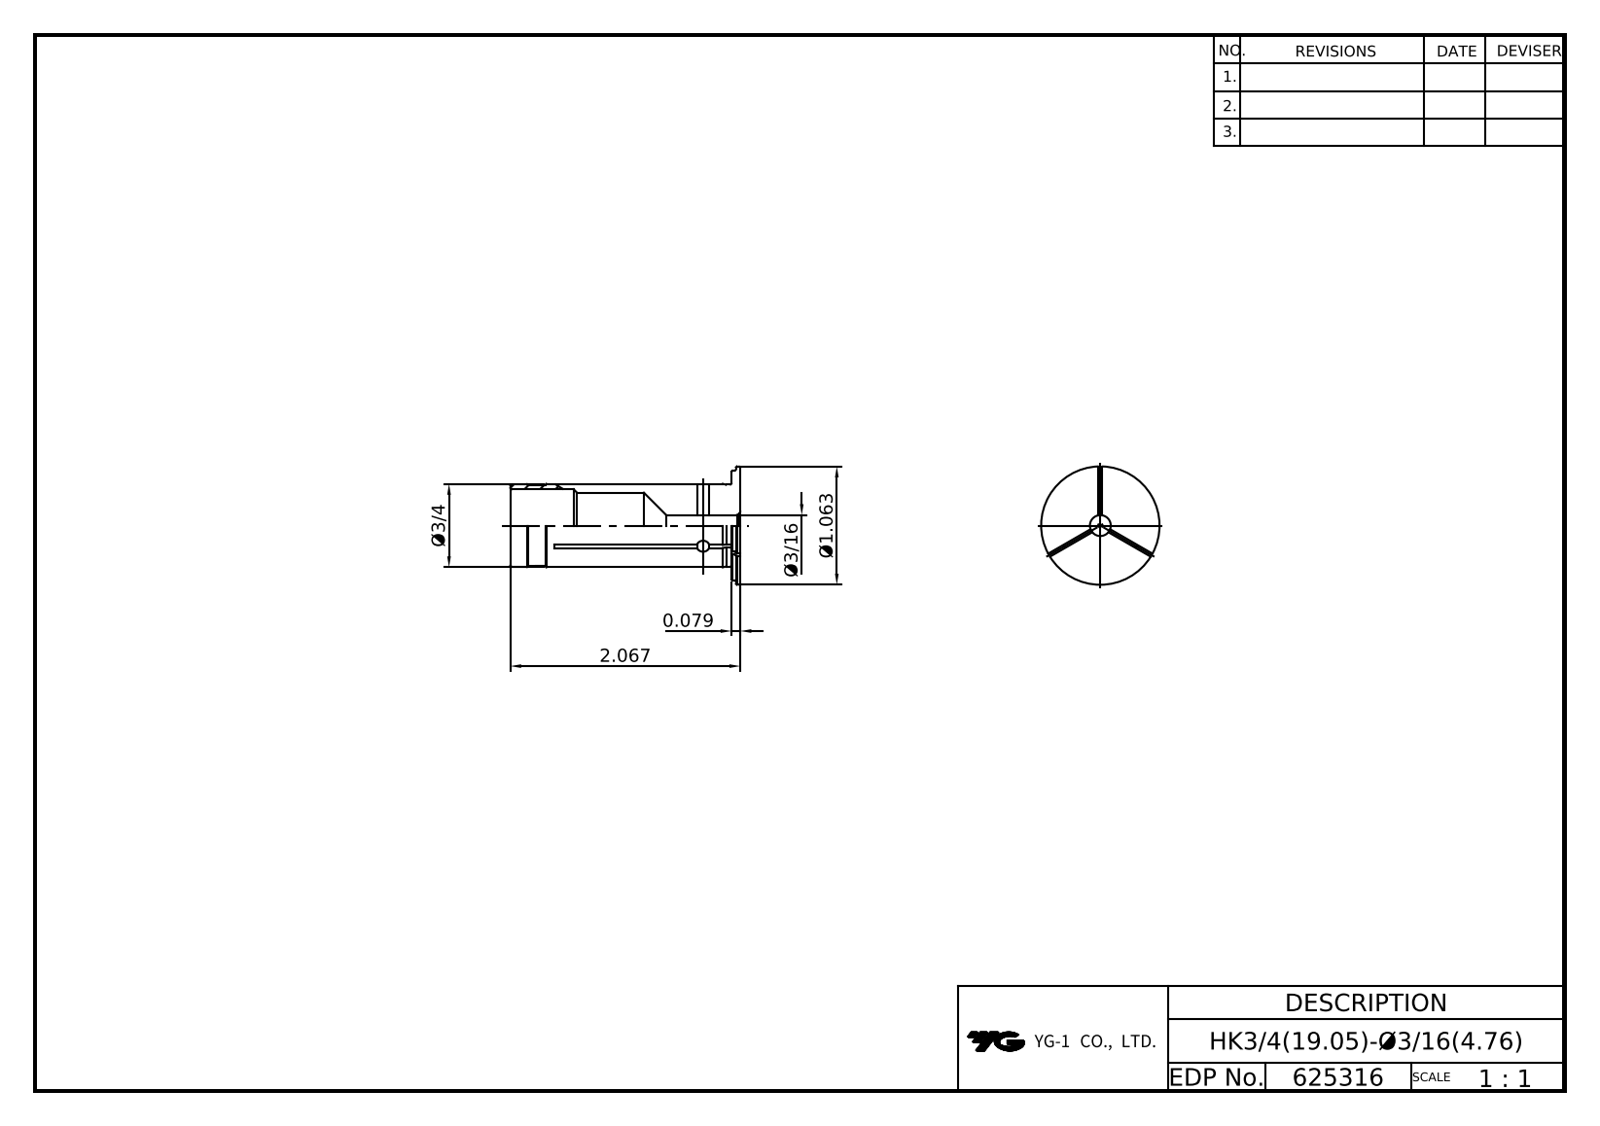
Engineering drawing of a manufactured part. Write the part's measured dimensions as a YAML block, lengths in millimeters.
part_name: "HK19_05-4_7625"
step_written_by: "PRO/ENGINEER BY PARAMETRIC TECHNOLOGY CORPORATION, 2012130 (CONFIG_CONTROL_DESIGN)"
units: millimeters
bodies: {solids: 1, faces: 92, planar: 22, cylindrical: 32, other: 38}
overall_size: [52.5, 27, 26.99]
volume: 8128
surface_area: 6928
round_holes:
  - {diameter: 2.9, count: 3}
  - {diameter: 4.76, count: 1}
  - {diameter: 15, count: 1}
  - {diameter: 16.5, count: 1}
round_bosses_or_shafts:
  - {diameter: 27, count: 1}
  - {diameter: 25, count: 1}
  - {diameter: 19.05, count: 1}
  - {diameter: 18.85, count: 1}
  - {diameter: 18.65, count: 1}
  - {diameter: 18.55, count: 1}
partial_cylinders:
  - {radius: 50, count: 3}
face_to_face_distances: [0.8, 2, 1, 50.5, 51.5, 52.5]
